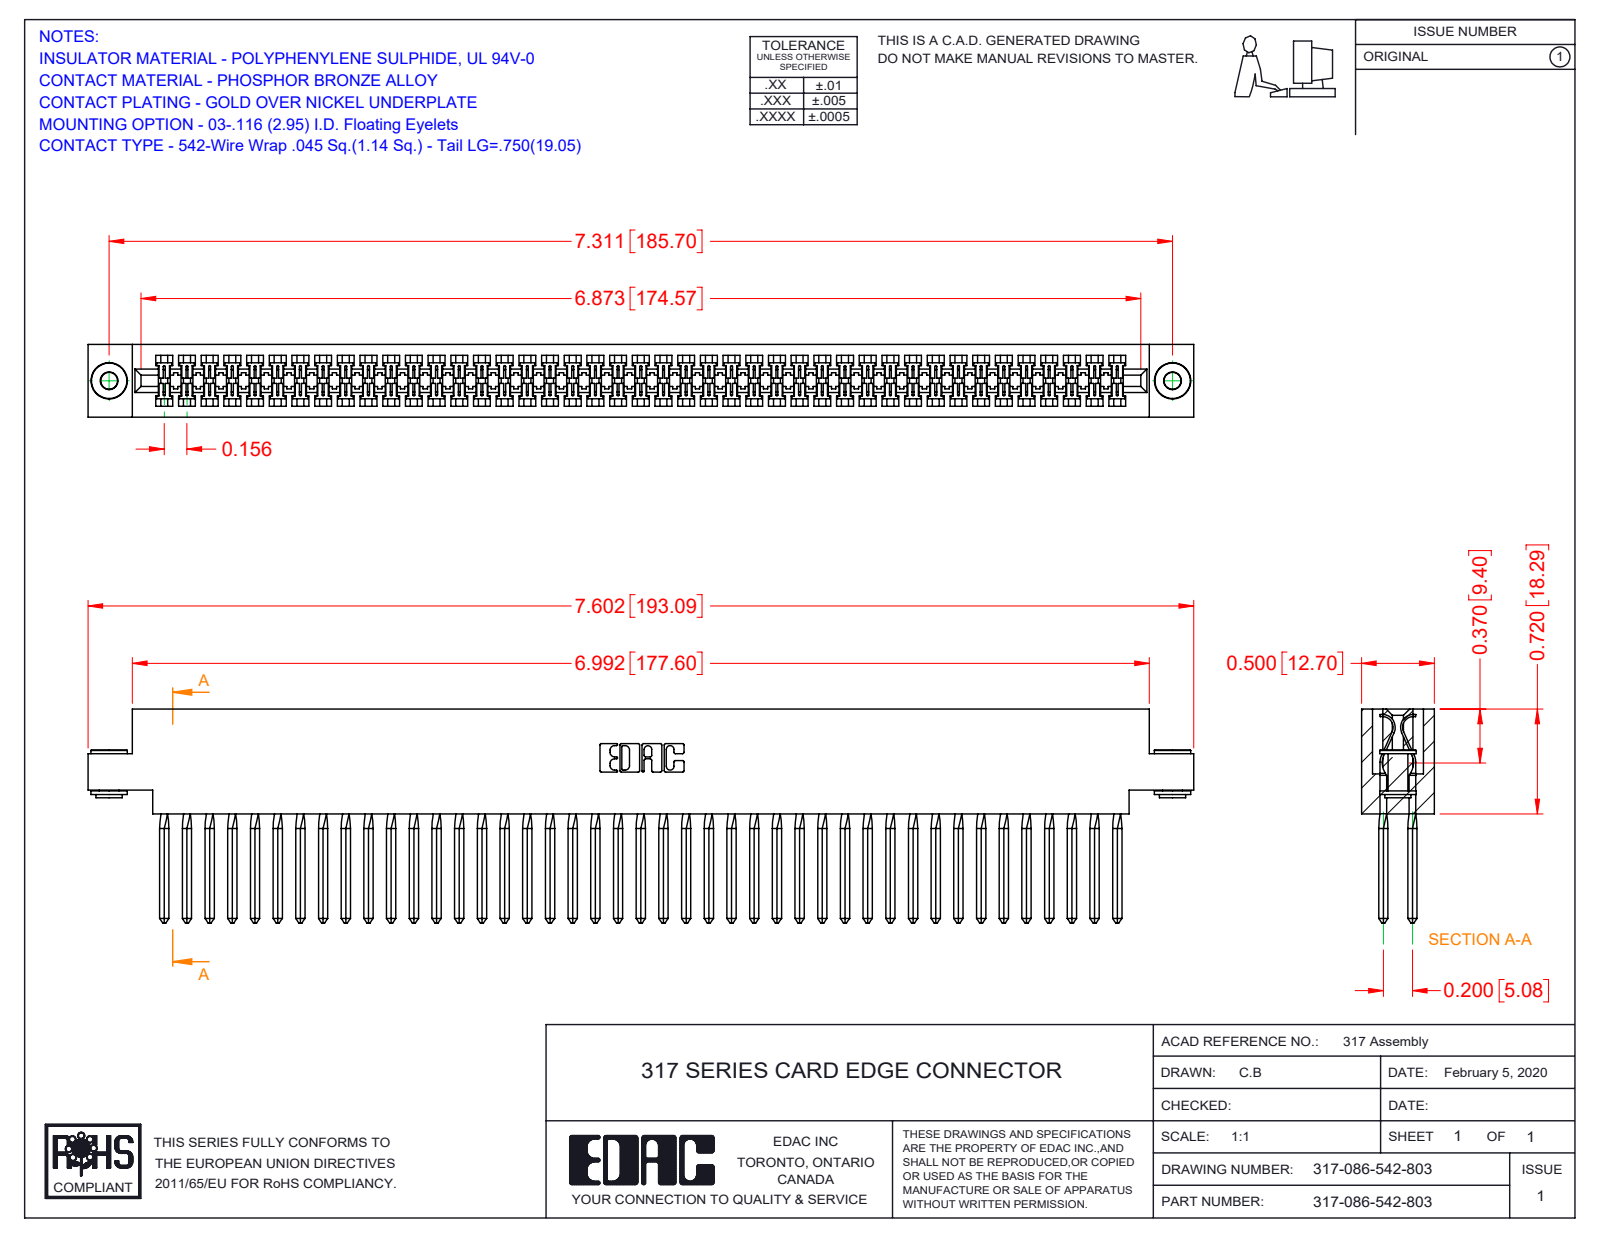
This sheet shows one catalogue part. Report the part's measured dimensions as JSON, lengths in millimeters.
{"part_name": "317-086-542-803; 317 Part_.156 Dia - TH; 317-290-003_542; 345-250-002_345-250-002-102", "step_written_by": "SolidWorks 2016 (CONFIG_CONTROL_DESIGN)", "units": "millimeters", "bodies": {"solids": 89, "faces": 5042, "planar": 4024, "cylindrical": 666, "other": 352}, "overall_size": [193.1, 37.3, 12.7], "volume_mm3": 31680, "surface_area_mm2": 44280, "round_holes": [[2.9, 2], [4, 2]], "round_bosses_or_shafts": [[6.4, 2], [4.6, 2], [3.5, 2]], "partial_cylinders_radius": [[0.2, 172], [0.3, 22], [0.2, 6], [0.8, 6], [0.7, 3], [1.9, 2], [2.3, 2], [2.5, 2]], "face_to_face_distances": [12.7, 1.9, 10.8, 8.9, 5.1, 1.2, 3.3, 9.4, 1.3, 7.5], "hole_center_spacings": [185.7]}
